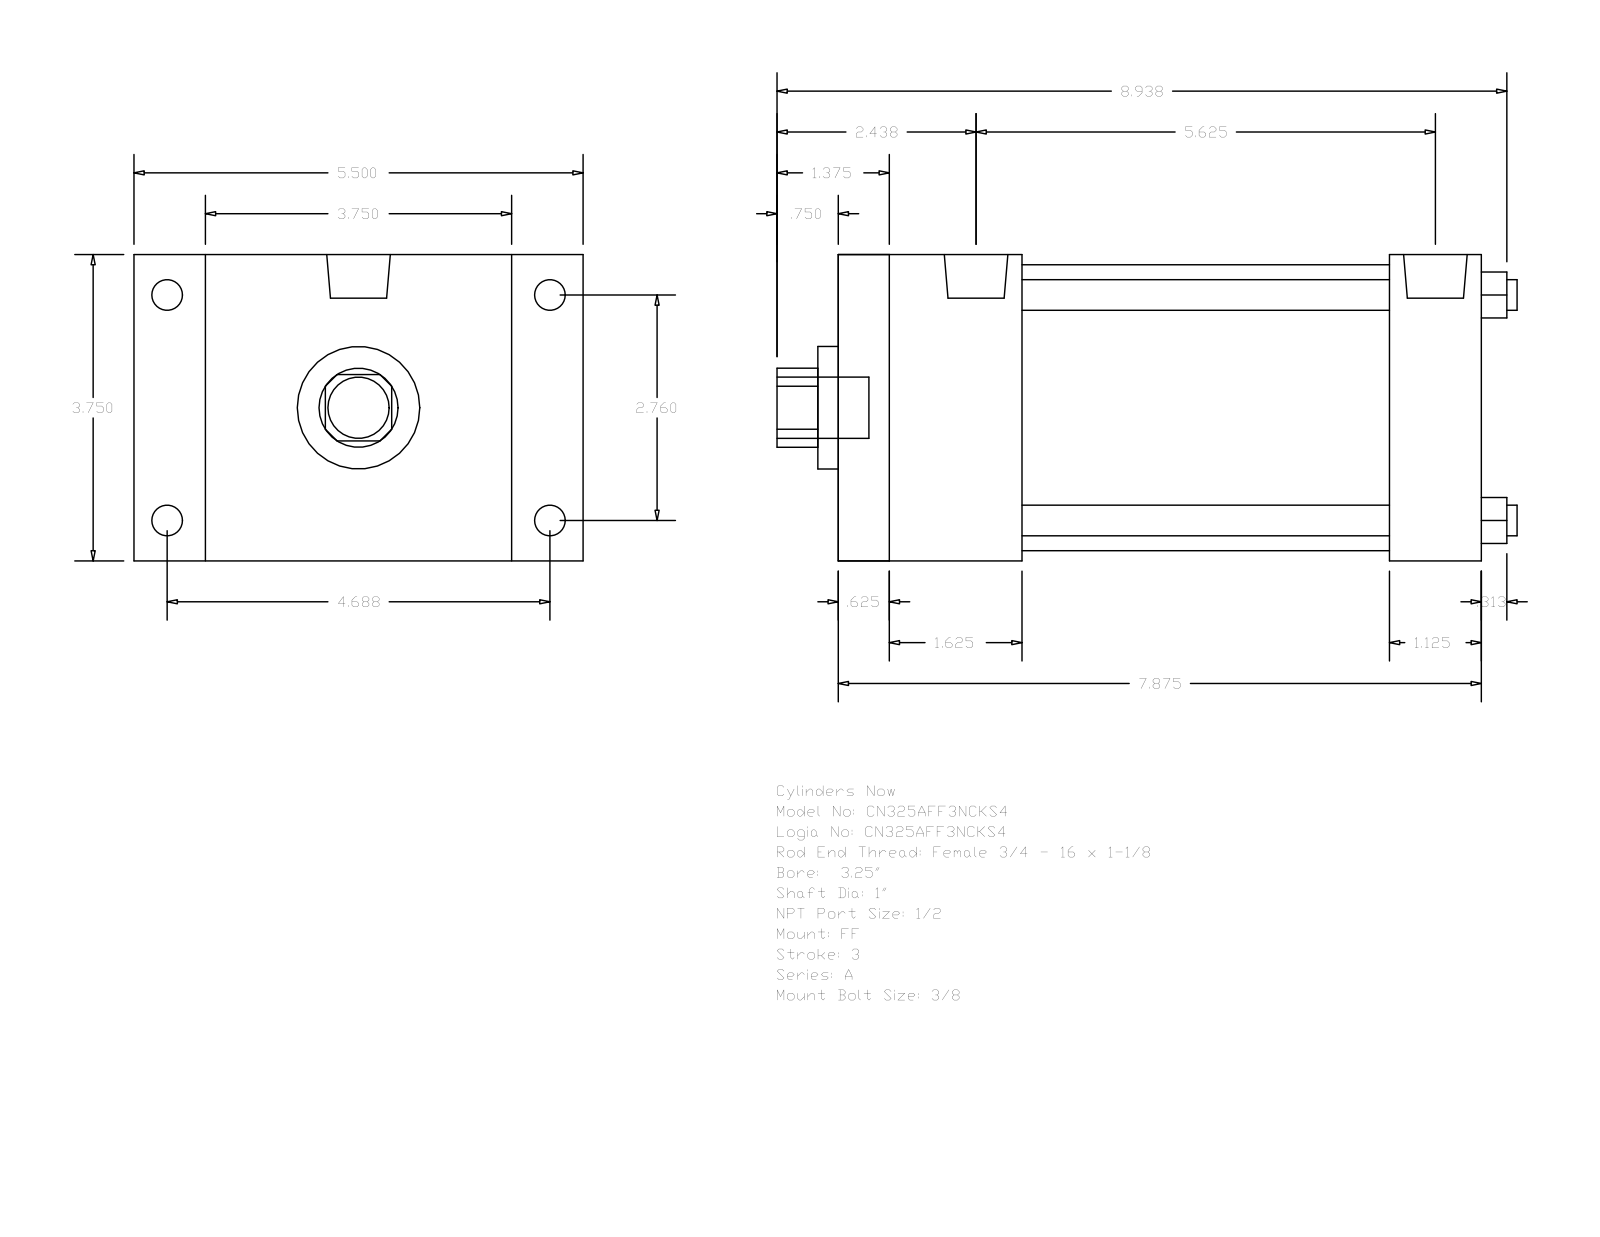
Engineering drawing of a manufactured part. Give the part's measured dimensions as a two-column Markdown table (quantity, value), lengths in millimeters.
| quantity | value |
| --- | --- |
| part name | A_FF__0325_1 |
| STEP written by | GSSL Pune (CONFIG_CONTROL_DESIGN) |
| units | millimeters |
| bodies | 0 solids, 92 faces (64 planar, 28 cylindrical, 0 other) |
| overall size | 230.19 × 139.7 × 95.25 |
| round holes (diameter × count) | 9.53 × 4, 25.4 × 1, 38.1 × 1, 88.9 × 1 |
| round bosses / shafts (diameter × count) | 9.53 × 4, 8.73 × 4, 19.77 × 2, 19.05 × 1 |
| partial cylindrical surfaces (radius × count) | 12.29 × 1 |
| main face-to-face distances | 95.24, 200.02, 15.87, 184.15, 22.23, 117.47, 28.57, 57.15, 171.45, 41.28 |
| hole center spacings | 49.57, 70.1, 99.14 |
